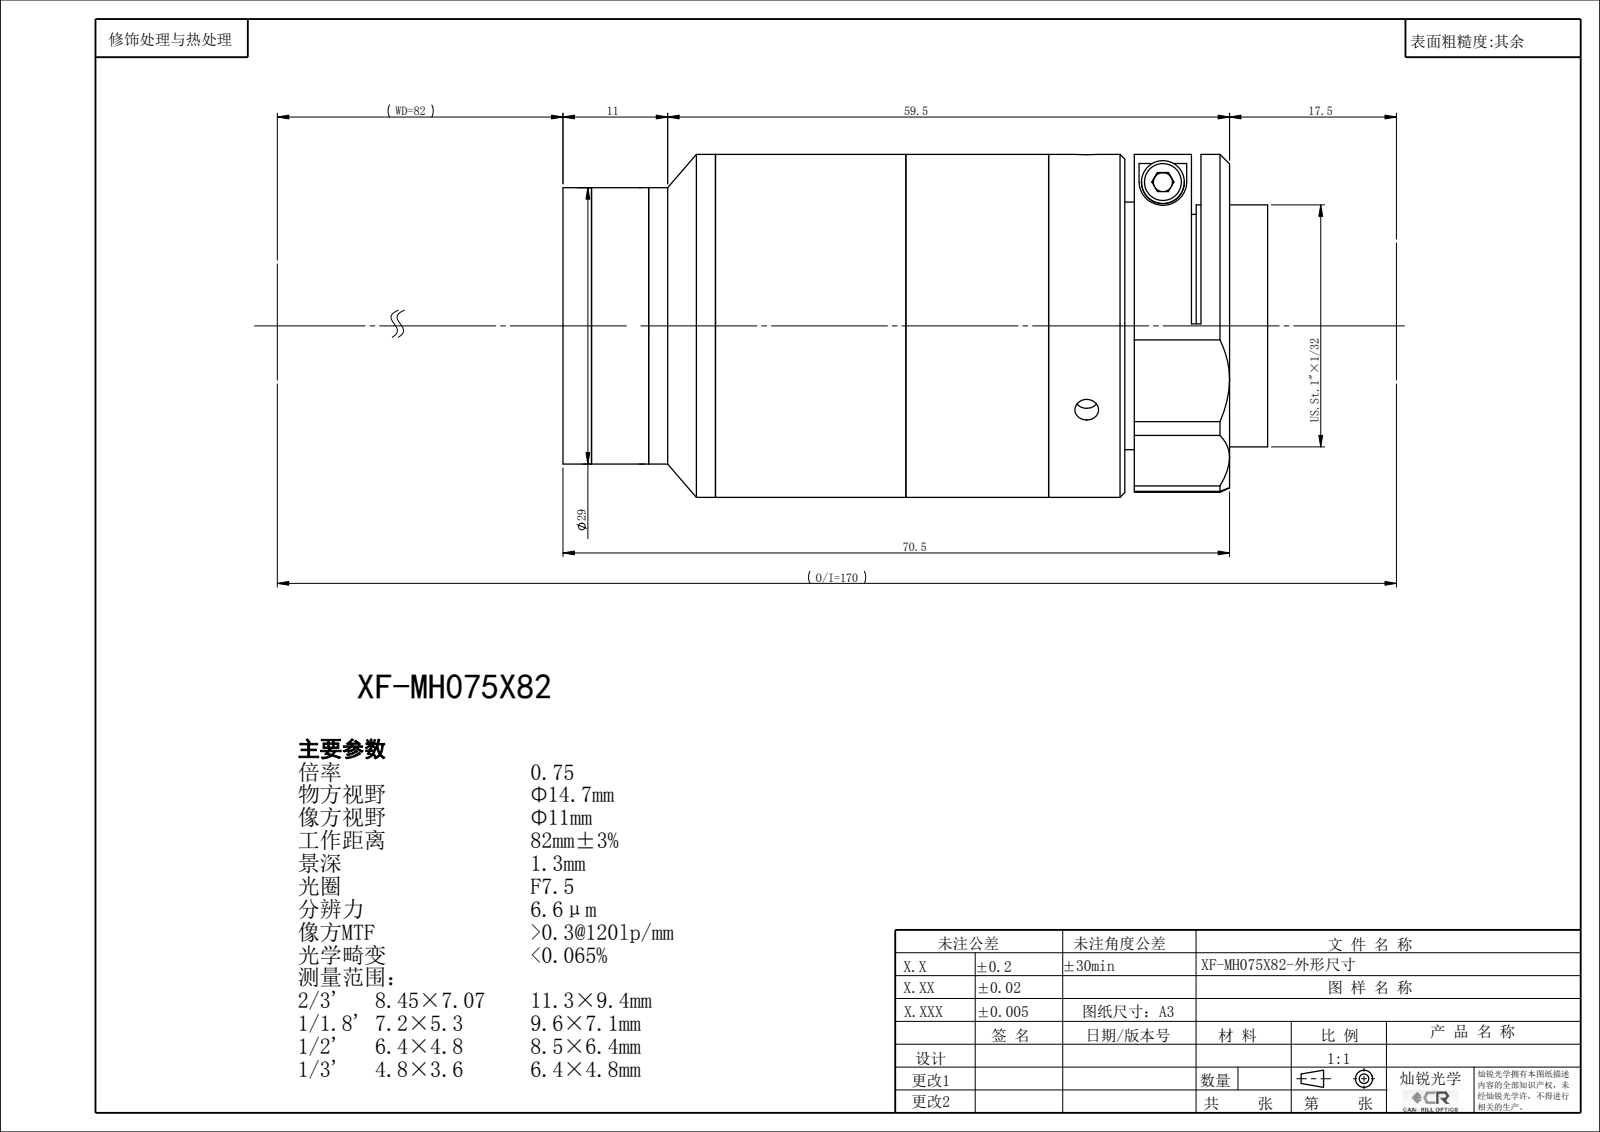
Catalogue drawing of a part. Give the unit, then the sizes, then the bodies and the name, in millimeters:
Units: millimetres
Overall size (bounding box): 74.52 × 36.01 × 36
Round holes (diameter × count): ⌀2.5 ×3, ⌀14 ×1, ⌀22.4 ×1, ⌀24 ×1, ⌀24.9 ×1, ⌀26.4 ×1, ⌀27 ×1
Round bosses / shafts (diameter × count): ⌀36 ×1, ⌀34 ×1, ⌀29 ×1, ⌀25.4 ×1
Main face-to-face distances: 1.5, 19.5, 47.22, 66.72, 16.5, 65.22, 18, 32.22, 15, 33
Bodies: 0 solids, 133 faces (69 planar, 42 cylindrical, 22 other)
Part name (STEP PRODUCT): XF-MH075X82
STEP written by: SolidWorks 2022 (CONFIG_CONTROL_DESIGN)
